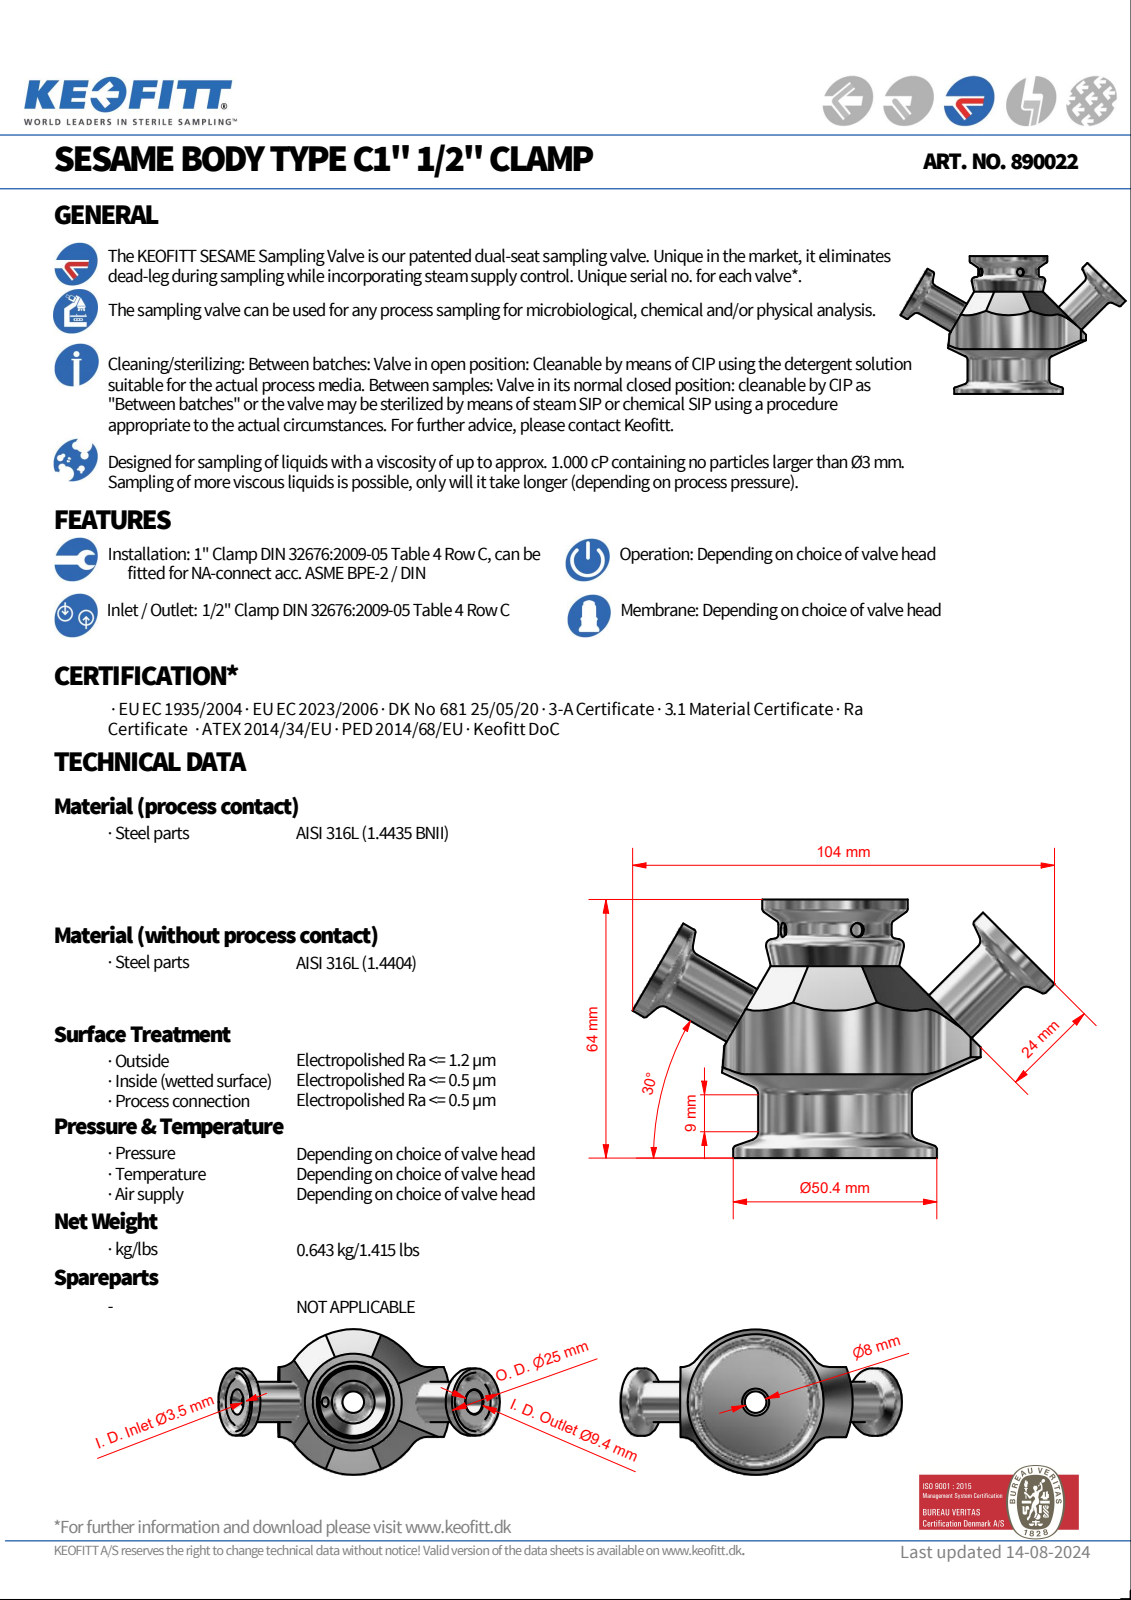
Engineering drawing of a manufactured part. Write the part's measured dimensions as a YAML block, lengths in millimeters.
part_name: "890022"
step_written_by: "Autodesk Inventor 2024 (AUTOMOTIVE_DESIGN)"
units: millimeters
bodies: {solids: 1, faces: 121, planar: 20, cylindrical: 37, other: 64}
overall_size: [104.23, 64, 54]
volume: 109039
surface_area: 17977
round_holes:
  - {diameter: 3.5, count: 2}
round_bosses_or_shafts:
  - {diameter: 25, count: 2}
  - {diameter: 15, count: 2}
  - {diameter: 50.5, count: 1}
  - {diameter: 38, count: 1}
  - {diameter: 36, count: 1}
  - {diameter: 28, count: 1}
partial_cylinders:
  - {radius: 7, count: 8}
  - {radius: 0.2, count: 7}
  - {radius: 13, count: 1}
  - {radius: 27, count: 1}
  - {radius: 36, count: 1}
face_to_face_distances: [64, 24, 47.5, 16.5, 26, 51.27]
